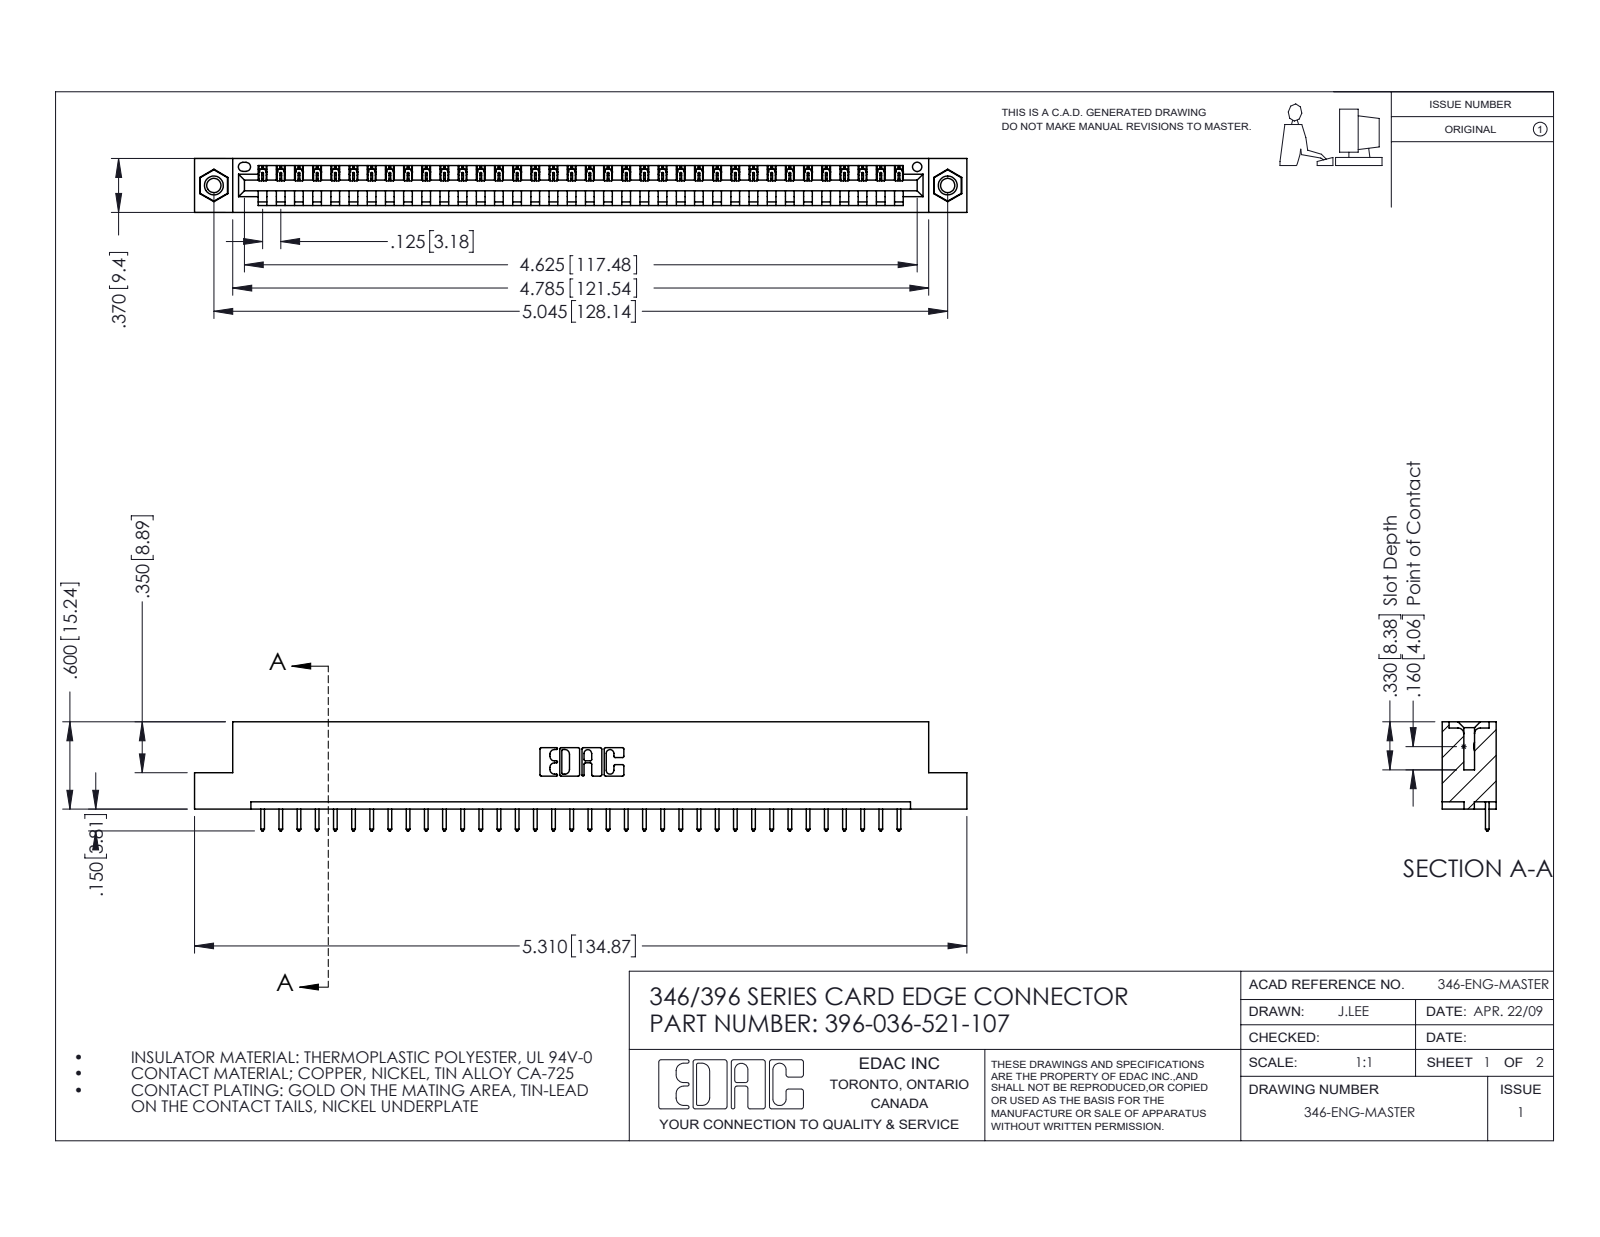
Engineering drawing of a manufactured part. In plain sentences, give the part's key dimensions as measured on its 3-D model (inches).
The part is named "346 Part_Flush Mounting Lugs - 0.156 Dia-TI; 345-250-001_345-250-005-103; 396-036-521-107; 345-292-001_345-293-121". Its 3-D file was written by "SolidWorks 2016 (CONFIG_CONTROL_DESIGN)". It is 39 solids with 2270 faces: 1548 planar, 706 cylindrical and 16 other. Overall it measures 5.31 by 0.75 by 0.37 inches. Its volume is 0.778 cubic inches and its surface area 24.03 square inches. Round holes: 2 of diameter 0.098, 2 of diameter 0.125, 2 of diameter 0.156, 1 of diameter 0.064. Round bosses or shafts: 2 of diameter 0.155. Partial cylindrical surfaces (rounded edges, fillets, slot ends): 72 of radius 0.006, 72 of radius 0.01, 22 of radius 0.01, 6 of radius 0.007, 6 of radius 0.031, 3 of radius 0.026, 2 of radius 0.031, 2 of radius 0.04. The main face-to-face distances are 0.048, 0.322, 0.37, 0.25, 0.072, 0.298, 0.025, 0.148, 0.222, 0.1. The hole center spacings are 0.246, 4.836, 5.045.
